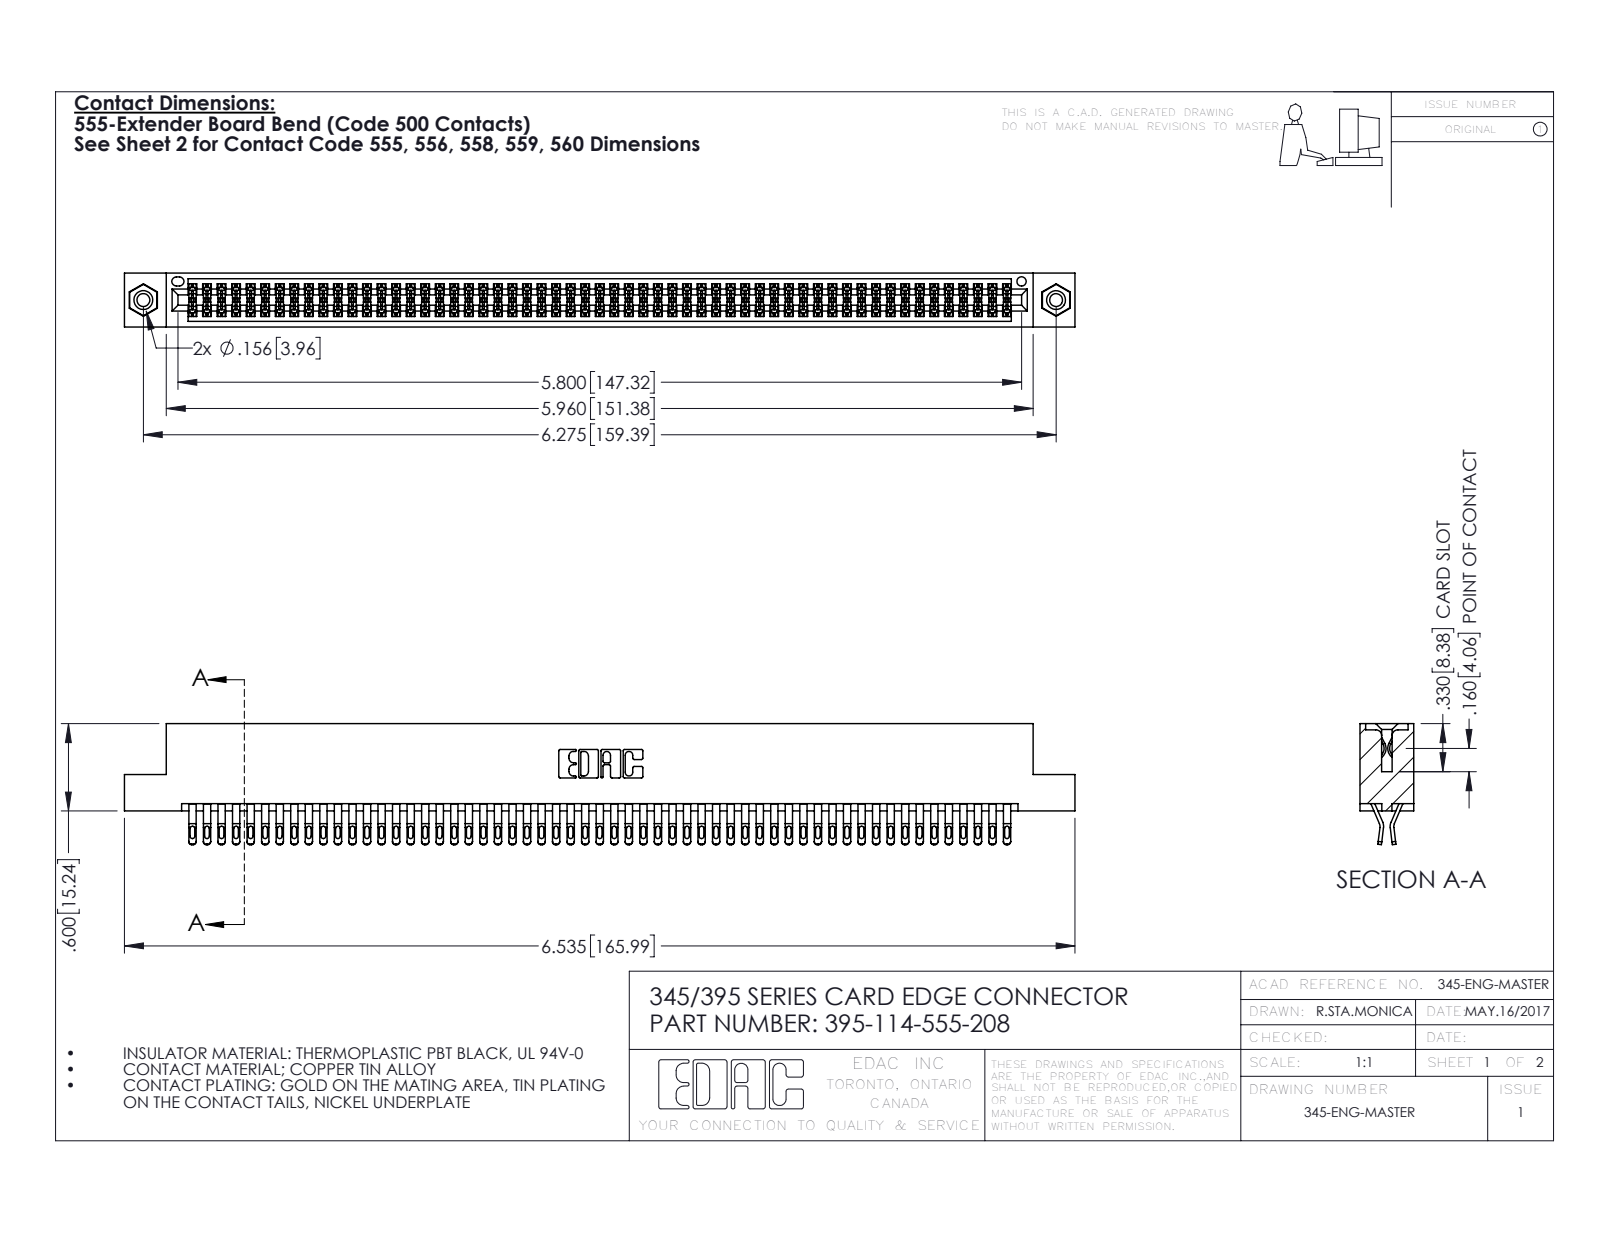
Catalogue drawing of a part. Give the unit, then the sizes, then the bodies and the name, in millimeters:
Units: millimetres
Overall size (bounding box): 166 × 21.1 × 9.4
Round holes (diameter × count): ⌀2.3 ×2, ⌀3.2 ×2, ⌀4 ×2, ⌀1.6 ×1
Round bosses / shafts (diameter × count): ⌀3.9 ×2
Partial cylindrical surfaces — rounded edges, fillets, slot ends (radius × count): R0.4 ×285, R0.5 ×228, R0.2 ×171, R0.3 ×22, R0.2 ×6, R0.8 ×6, R0.7 ×3, R0.3 ×2
Main face-to-face distances: 1.8, 7.6, 0.6, 9.4, 5.1, 2.5, 6.9, 5.7, 4.4, 3.8
Hole centre spacings: 6.9, 153.4, 159.4
Volume: 16 580 mm³ · Surface area: 25 970 mm²
Bodies: 117 solids, 6570 faces (3646 planar, 2908 cylindrical, 16 other)
Part name (STEP PRODUCT): 345-292-001_555 Tail; 345-250-001_345-250-003-102; 345 Part_Flush Mounting Lugs - 0.156 Dia-TI; 395-114-555-208
STEP written by: SolidWorks 2016 (CONFIG_CONTROL_DESIGN)
